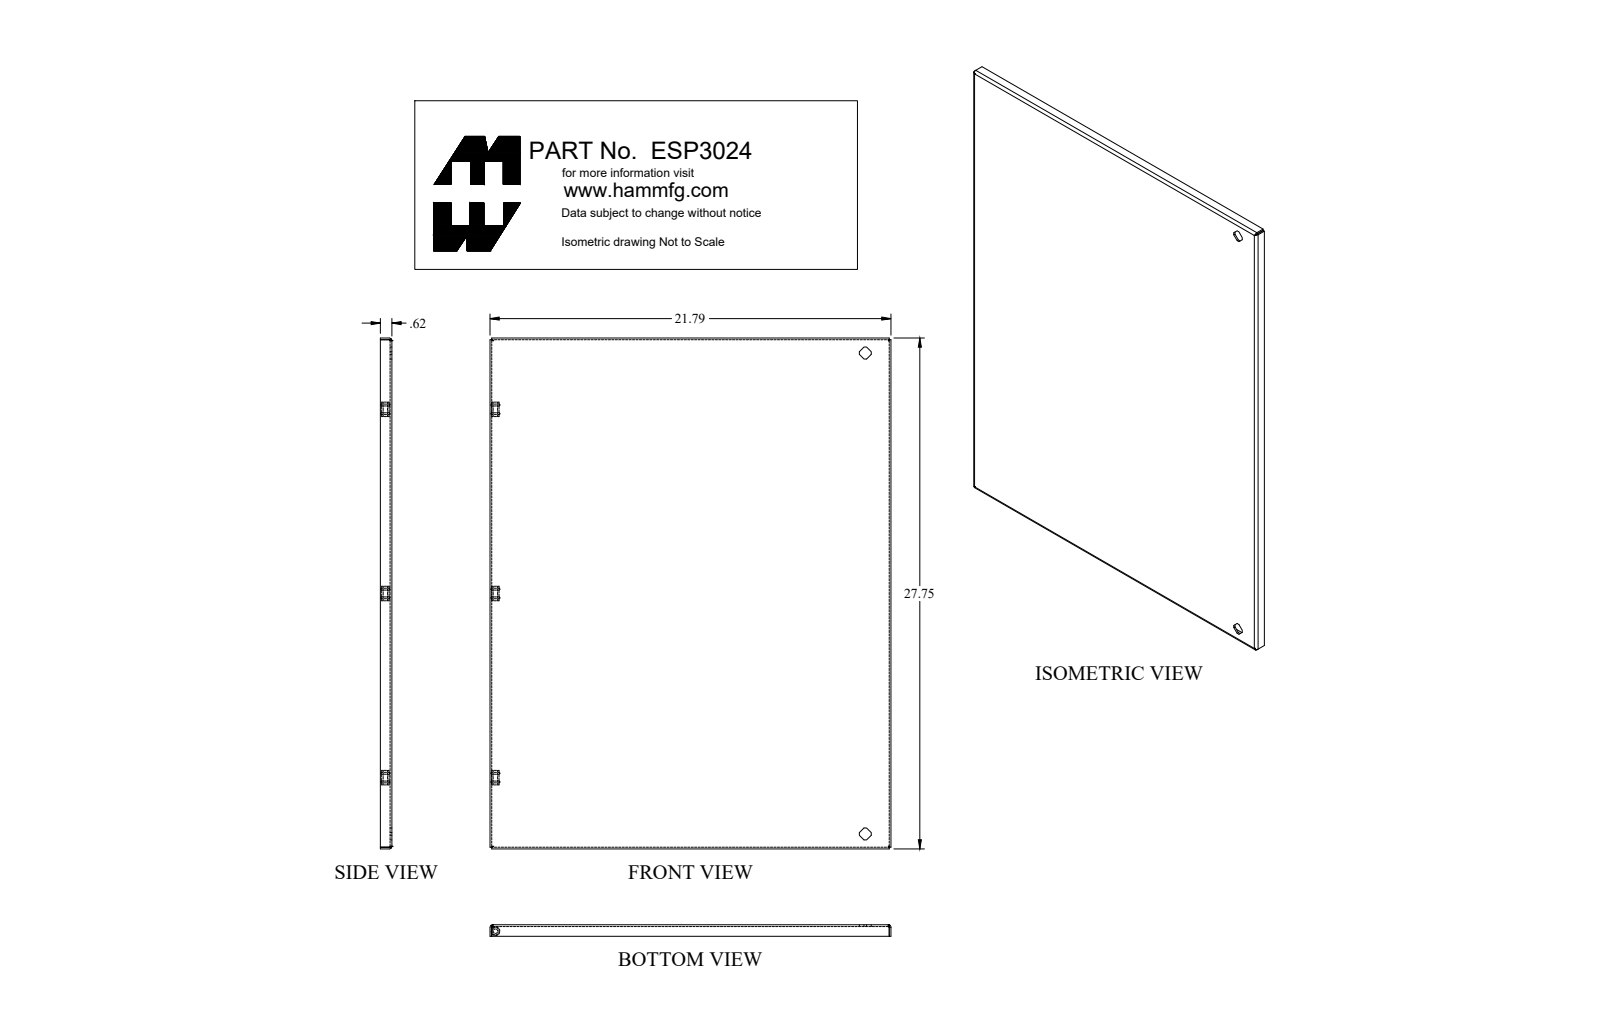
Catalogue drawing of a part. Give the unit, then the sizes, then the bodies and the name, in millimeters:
Units: millimetres
Overall size (bounding box): 704.9 × 605.9 × 233.8
Round holes (diameter × count): ⌀3.5 ×3, ⌀6.1 ×3, ⌀13.1 ×2
Round bosses / shafts (diameter × count): ⌀5.9 ×6, ⌀9 ×3, ⌀20 ×2, ⌀13.6 ×2, ⌀12.6 ×2, ⌀11 ×2
Partial cylindrical surfaces — rounded edges, fillets, slot ends (radius × count): R1.2 ×28, R0.3 ×24, R0.9 ×6, R2.7 ×6, R1.5 ×4, R3.6 ×4, R3.9 ×4, R4 ×4
Main face-to-face distances: 2.4, 1.8, 562.8, 20.7, 564.6, 1, 1, 19.8, 22.2, 21.6
Hole centre spacings: 254, 508, 664.4
Volume: 1 311 000 mm³ · Surface area: 1 241 000 mm²
Bodies: 14 solids, 634 faces (376 planar, 190 cylindrical, 68 other)
Part name (STEP PRODUCT): ESP3024
STEP written by: SolidWorks 2018 (AUTOMOTIVE_DESIGN)
